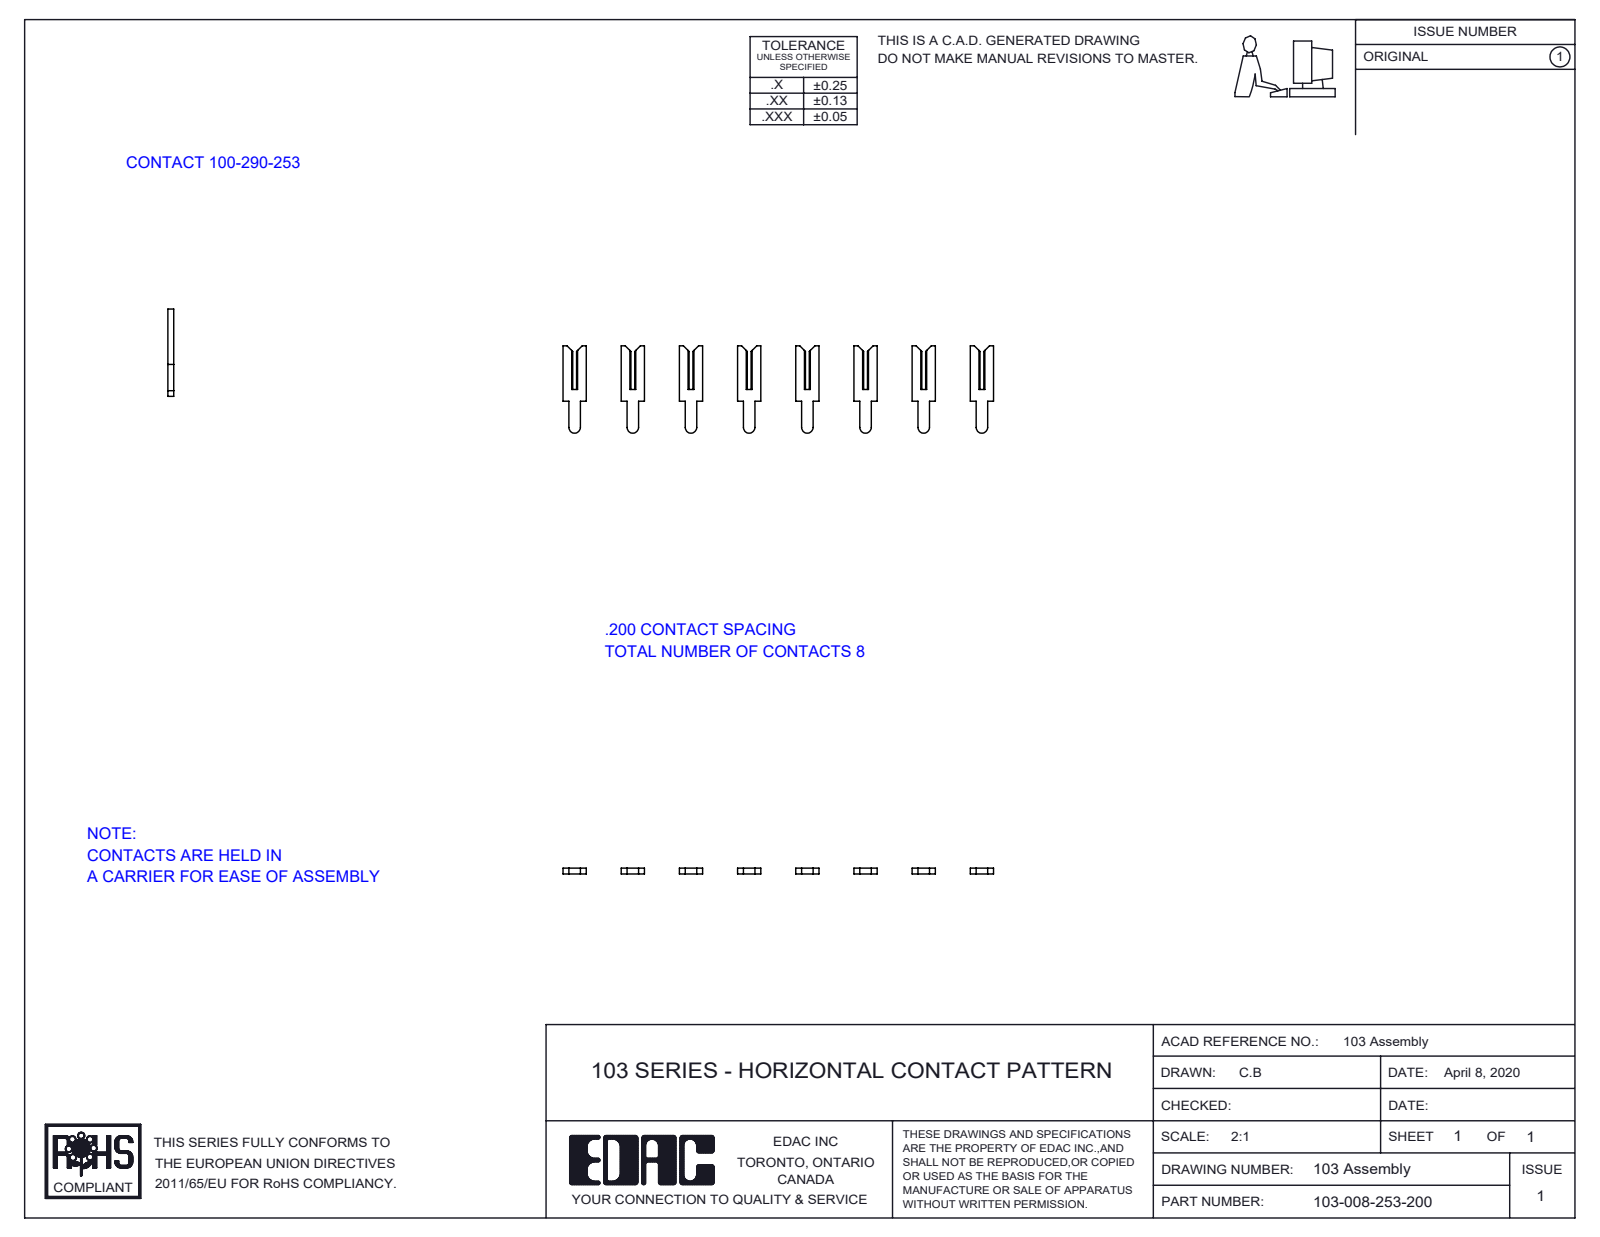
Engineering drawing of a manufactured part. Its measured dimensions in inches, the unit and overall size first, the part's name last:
Units: inches
Overall size (bounding box): 1.48 × 0.3 × 0.02
Partial cylindrical surfaces — rounded edges, fillets, slot ends (radius × count): R0.019 ×8
Main face-to-face distances: 0.02, 0.2, 0.4, 0.6, 0.8, 0.08, 0.28, 0.12, 1, 0.48
Volume: 0.003 in³ · Surface area: 0.427 in²
Bodies: 8 solids, 160 faces (152 planar, 8 cylindrical, 0 other)
Part name (STEP PRODUCT): 100-290-001_100-290-253; 103-008-253-200
STEP written by: SolidWorks 2016 (CONFIG_CONTROL_DESIGN)
